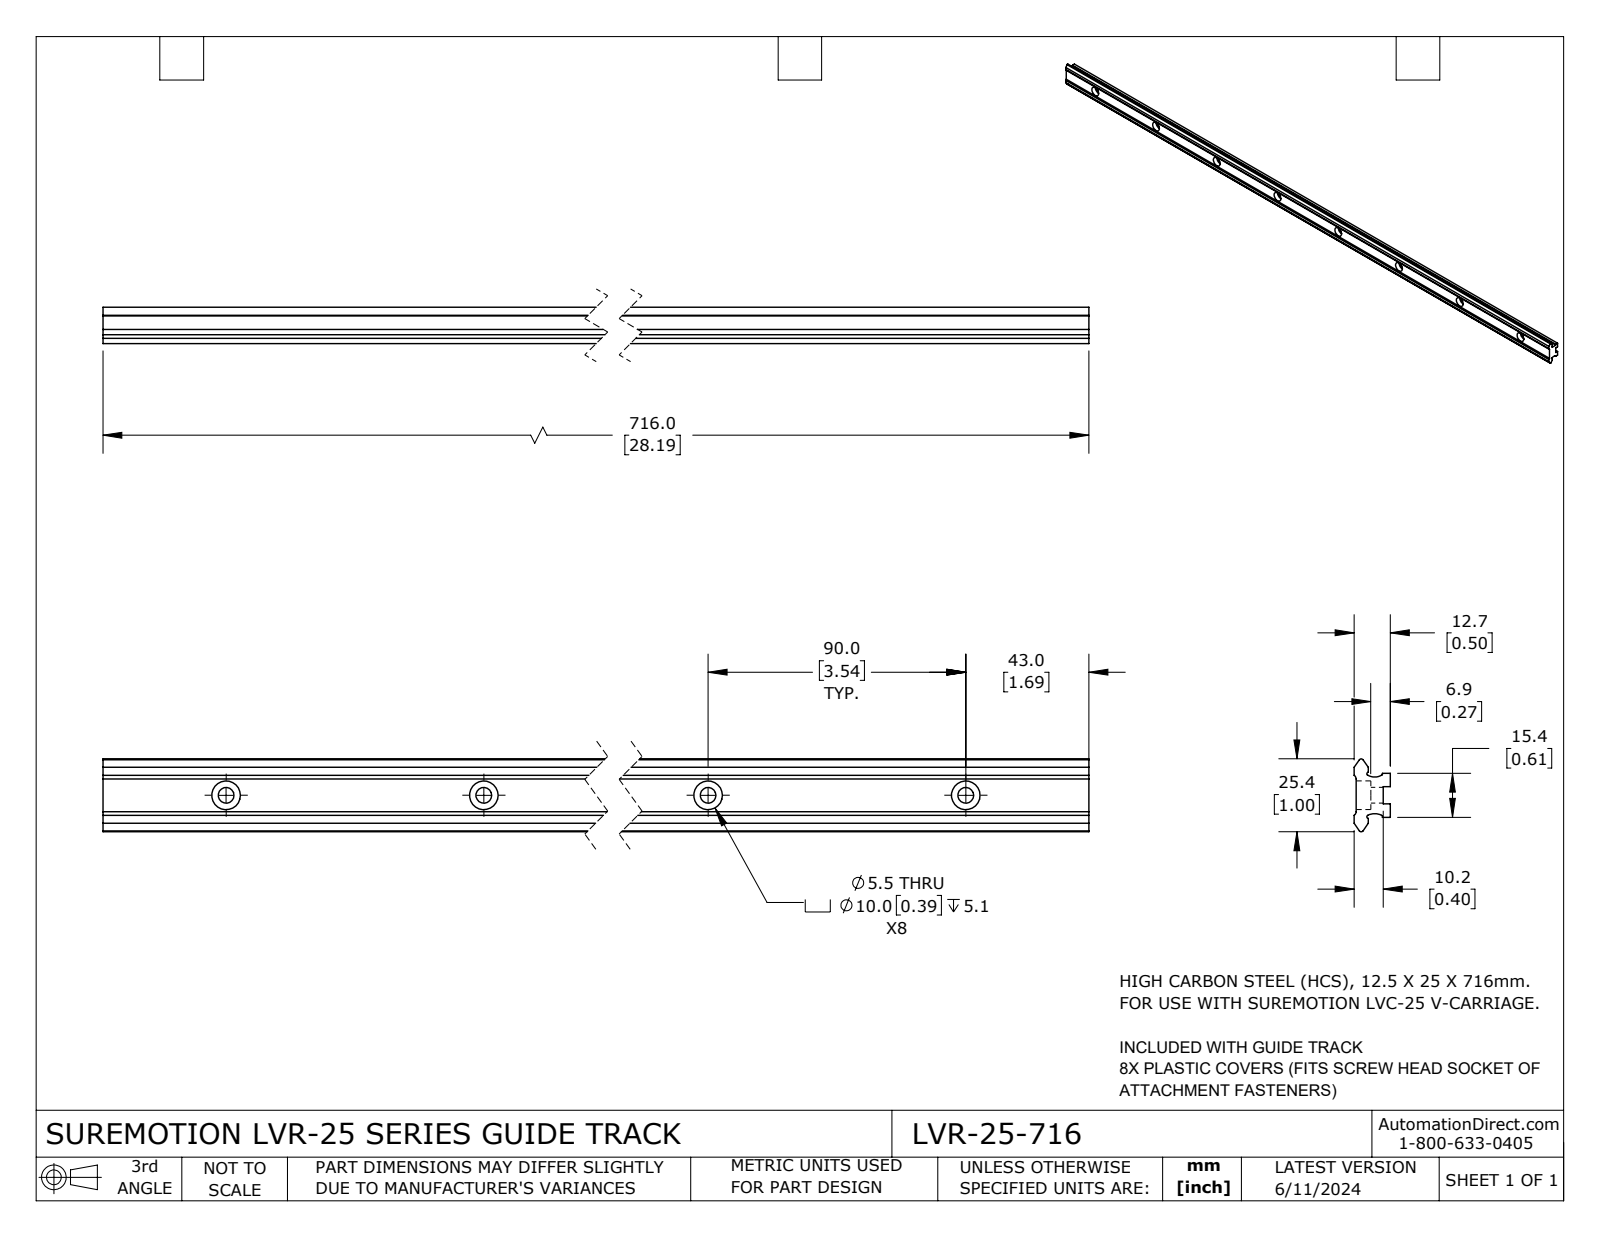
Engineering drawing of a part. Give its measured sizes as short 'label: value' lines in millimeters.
name: LVR-25-716
written by: SolidWorks 2023 (CONFIG_CONTROL_DESIGN)
unit: mm
bodies: 1 solid, 70 faces (26 planar, 44 cylindrical, 0 other)
size: 716 × 25.45 × 12.66
volume: 136 497 mm³; area: 59 081 mm²
holes: 8× ⌀5.5, 8× ⌀10
rounds: 4× R0.55, 2× R0.76, 2× R1.5, 2× R5.22
face distances: 11.96, 15.25, 2.5, 9.46, 12.66, 10.16, 0.7, 4.7, 10.7, 7.73
hole spacings: 90, 180, 270, 360, 450, 540, 630
